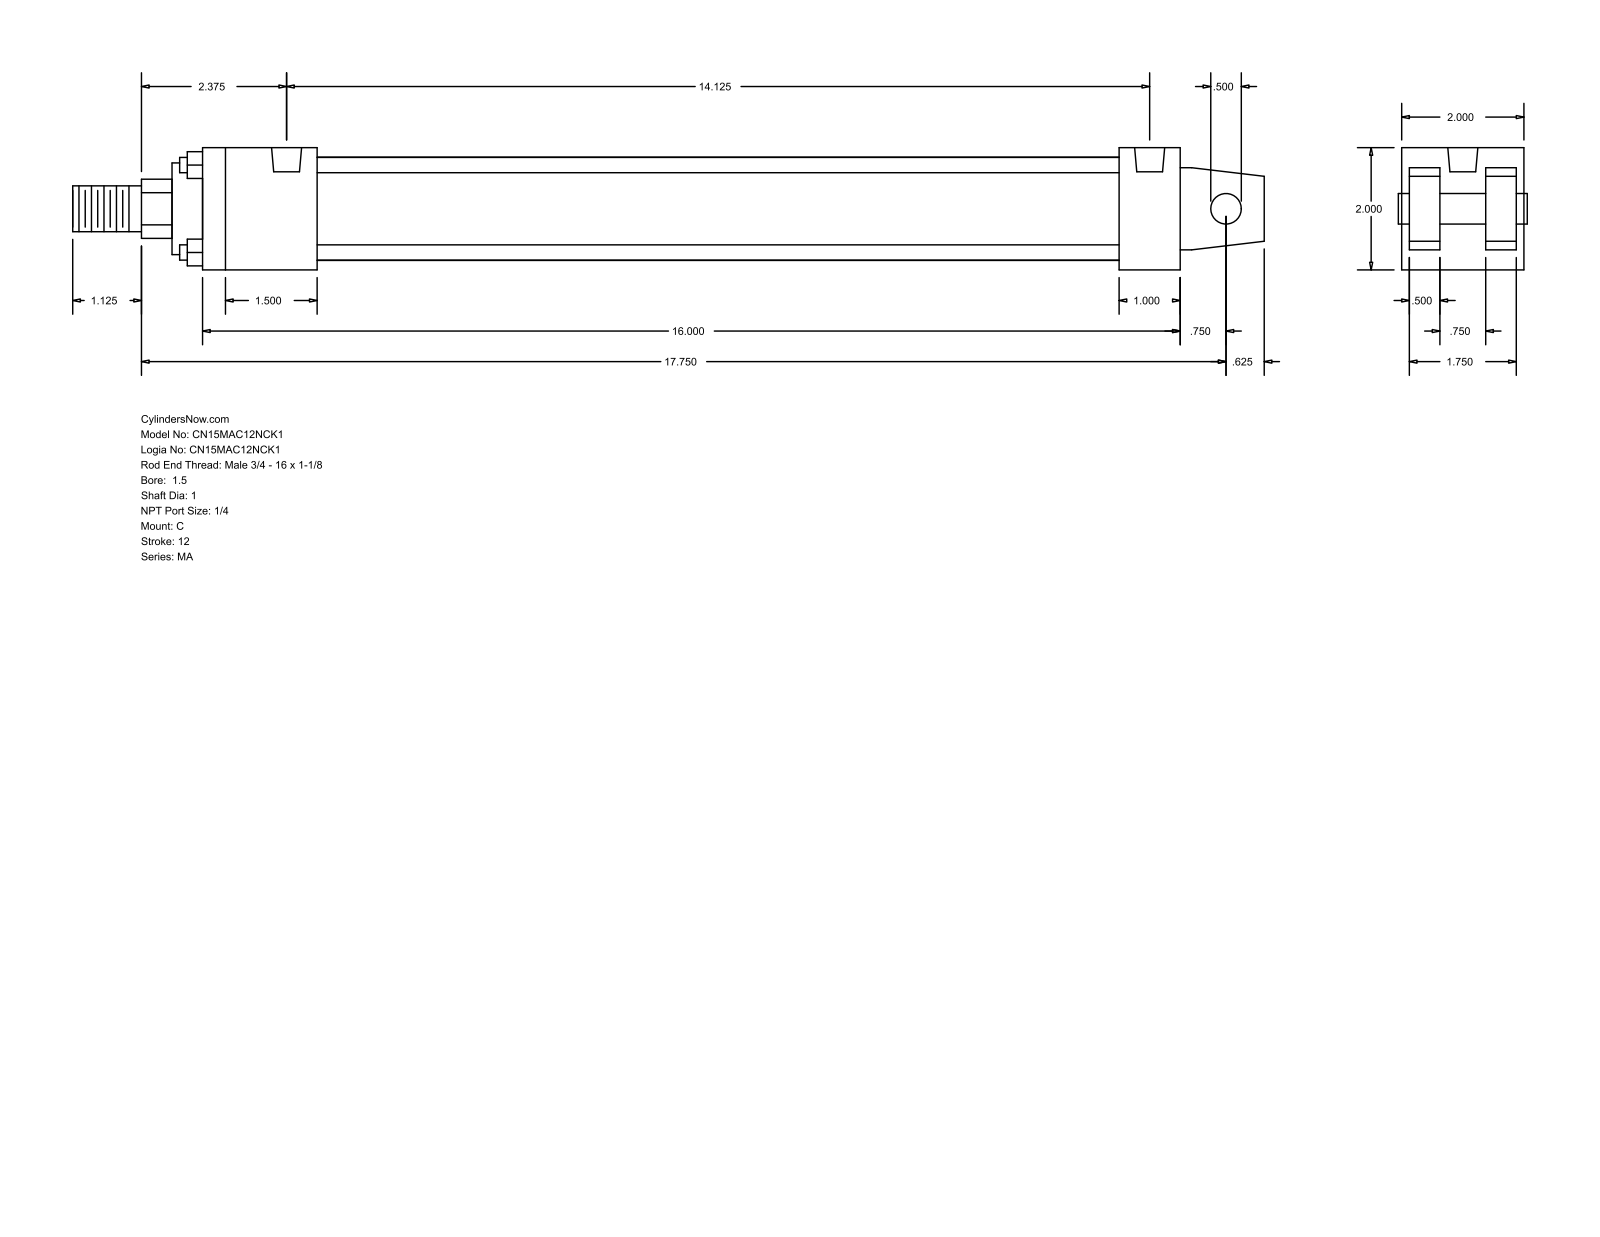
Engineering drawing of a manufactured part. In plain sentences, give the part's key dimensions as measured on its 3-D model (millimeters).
The part is named "MA_C__0150_1". Its 3-D file was written by "GSSL Pune (CONFIG_CONTROL_DESIGN)". It is 0 solids with 103 faces: 76 planar, 27 cylindrical and 0 other. Overall it measures 495.3 by 50.8 by 50.8 millimeters. Round holes: 4 of diameter 7.94, 2 of diameter 12.49. Round bosses or shafts: 4 of diameter 6.35, 1 of diameter 42.93, 1 of diameter 38.1, 1 of diameter 25.4, 1 of diameter 19.05, 1 of diameter 12.7. Partial cylindrical surfaces (rounded edges, fillets, slot ends): 1 of radius 12.29. The main face-to-face distances are 50.8, 47.63, 12.7, 34.93, 3.17, 15.87, 31.76, 60.33, 393.7, 406.4. The hole center spacings are 358.77.
